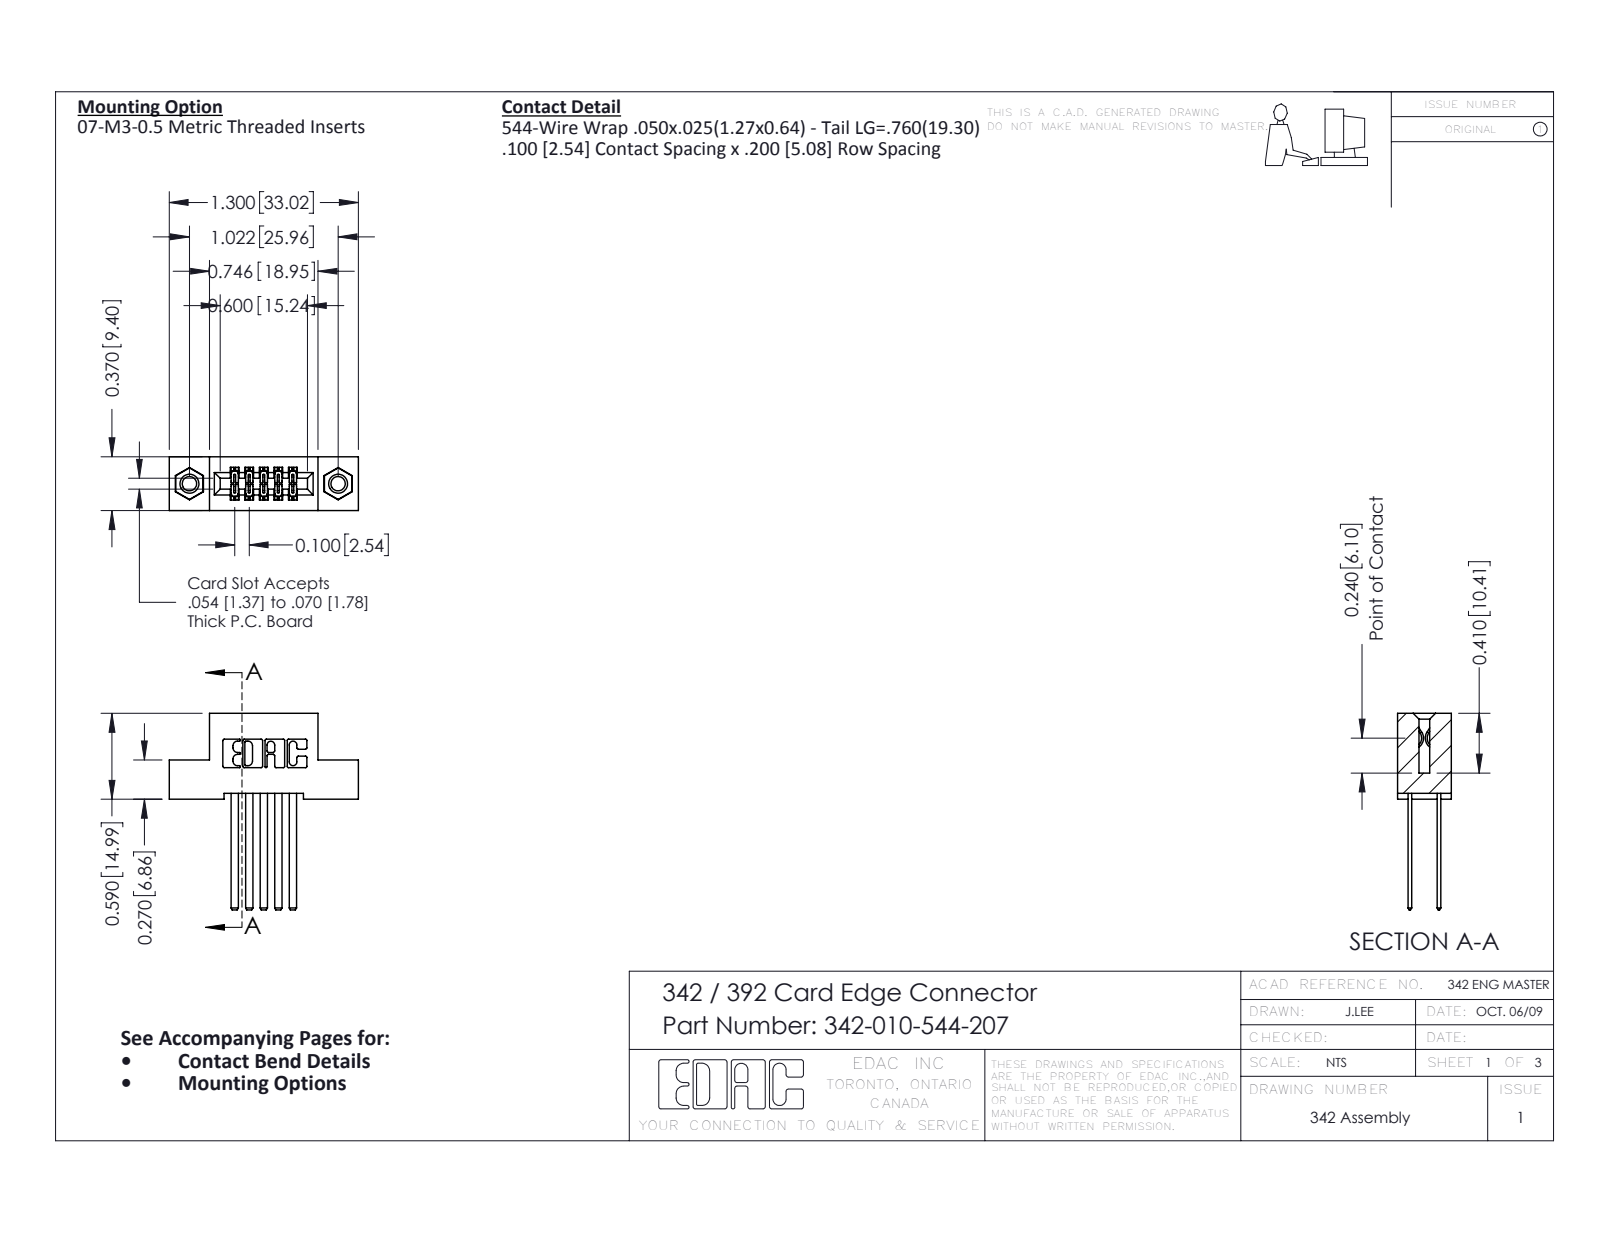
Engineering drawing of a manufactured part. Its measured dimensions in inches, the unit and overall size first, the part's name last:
Units: inches
Overall size (bounding box): 1.35 × 1.3 × 0.37
Round holes (diameter × count): ⌀0.098 ×2, ⌀0.125 ×2, ⌀0.156 ×2
Round bosses / shafts (diameter × count): ⌀0.155 ×2
Partial cylindrical surfaces — rounded edges, fillets, slot ends (radius × count): R0.01 ×22, R0.006 ×15, R0.007 ×6, R0.031 ×6, R0.026 ×3, R0.014 ×2, R0.022 ×2, R0.024 ×2
Main face-to-face distances: 0.2, 0.072, 0.298, 0.1, 0.098, 0.272, 0.025, 0.37, 0.04, 0.225
Hole centre spacings: 1.022
Volume: 0.178 in³ · Surface area: 6.594 in²
Bodies: 13 solids, 630 faces (418 planar, 196 cylindrical, 16 other)
Part name (STEP PRODUCT): 345-292-001_345-293-144; 342-010-544-207; 345-250-001_345-250-005-103; 342 Part_TI
STEP written by: SolidWorks 2016 (CONFIG_CONTROL_DESIGN)
